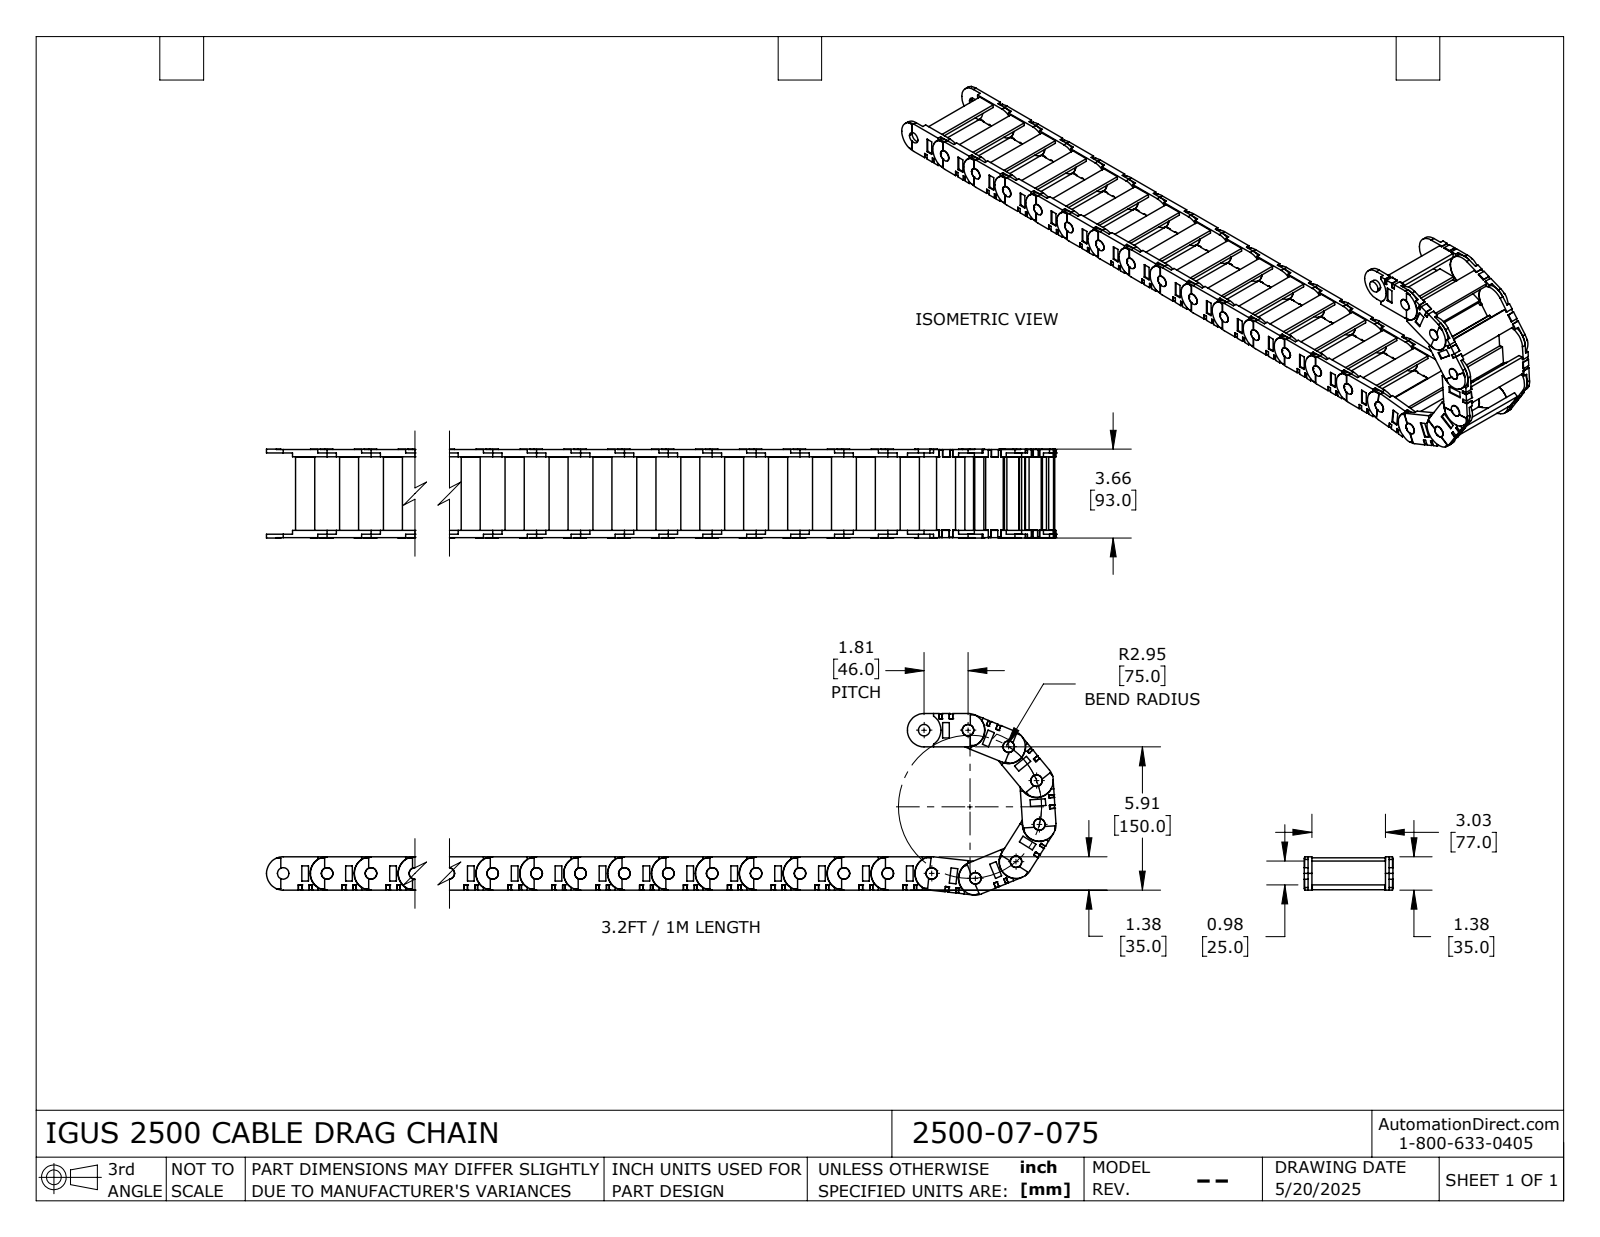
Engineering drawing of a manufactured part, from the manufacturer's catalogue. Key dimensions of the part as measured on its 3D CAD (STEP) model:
Part name (STEP PRODUCT): 2500_07_075
STEP written by: SolidWorks 2024 (AUTOMOTIVE_DESIGN)
Units: inches
Bodies: 66 solids, 2398 faces (1870 planar, 528 cylindrical, 0 other)
Overall size (bounding box): 32.981 × 7.485 × 3.661
Volume: 49.69 in³ · Surface area: 729.9 in²
Round holes (diameter × count): ⌀0.473 ×22
Round bosses / shafts (diameter × count): ⌀0.472 ×22, ⌀1.378 ×21
Partial cylindrical surfaces — rounded edges, fillets, slot ends (radius × count): R0.697 ×23, R0.689 ×2
Main face-to-face distances: 0.157, 3.189, 3.346, 0.142, 0.299, 3.331, 3.488, 0.197, 0.984, 3.031
Hole centre spacings: 1.811, 3.622, 5.433, 7.244, 9.055, 10.866, 12.677, 14.488
